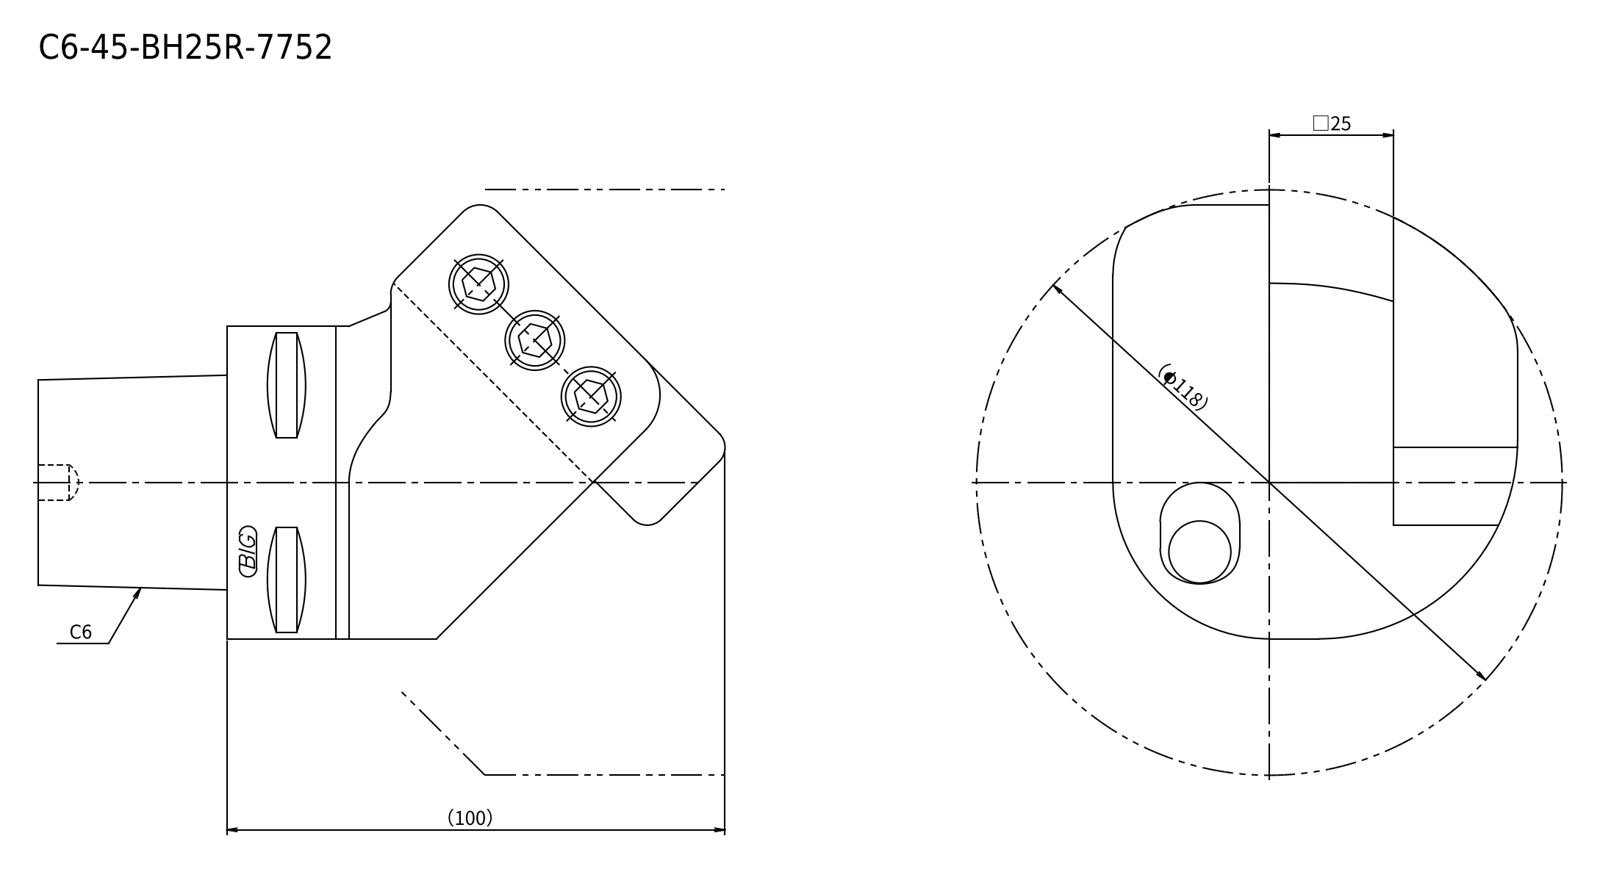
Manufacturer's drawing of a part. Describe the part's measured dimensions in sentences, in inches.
The part is named "240[2]". Its 3-D file was written by "Kubotek KeyCreator 2011 V10.0.2 (22737) (automotive_design)". It is 1 solid with 24 faces: 14 planar, 5 cylindrical and 5 other. Overall it measures 5.512 by 3.525 by 3.209 inches. Its volume is 21.74 cubic inches and its surface area 55.75 square inches. Round bosses or shafts: 1 of diameter 2.48. Partial cylindrical surfaces (rounded edges, fillets, slot ends): 1 of radius 1.24, 1 of radius 1.575, 1 of radius 2.323. The main face-to-face distances are 0.984, 2.224, 1.24, 0.984, 1.496, 3.209, 1.969, 1.299, 2.795, 0.59.
